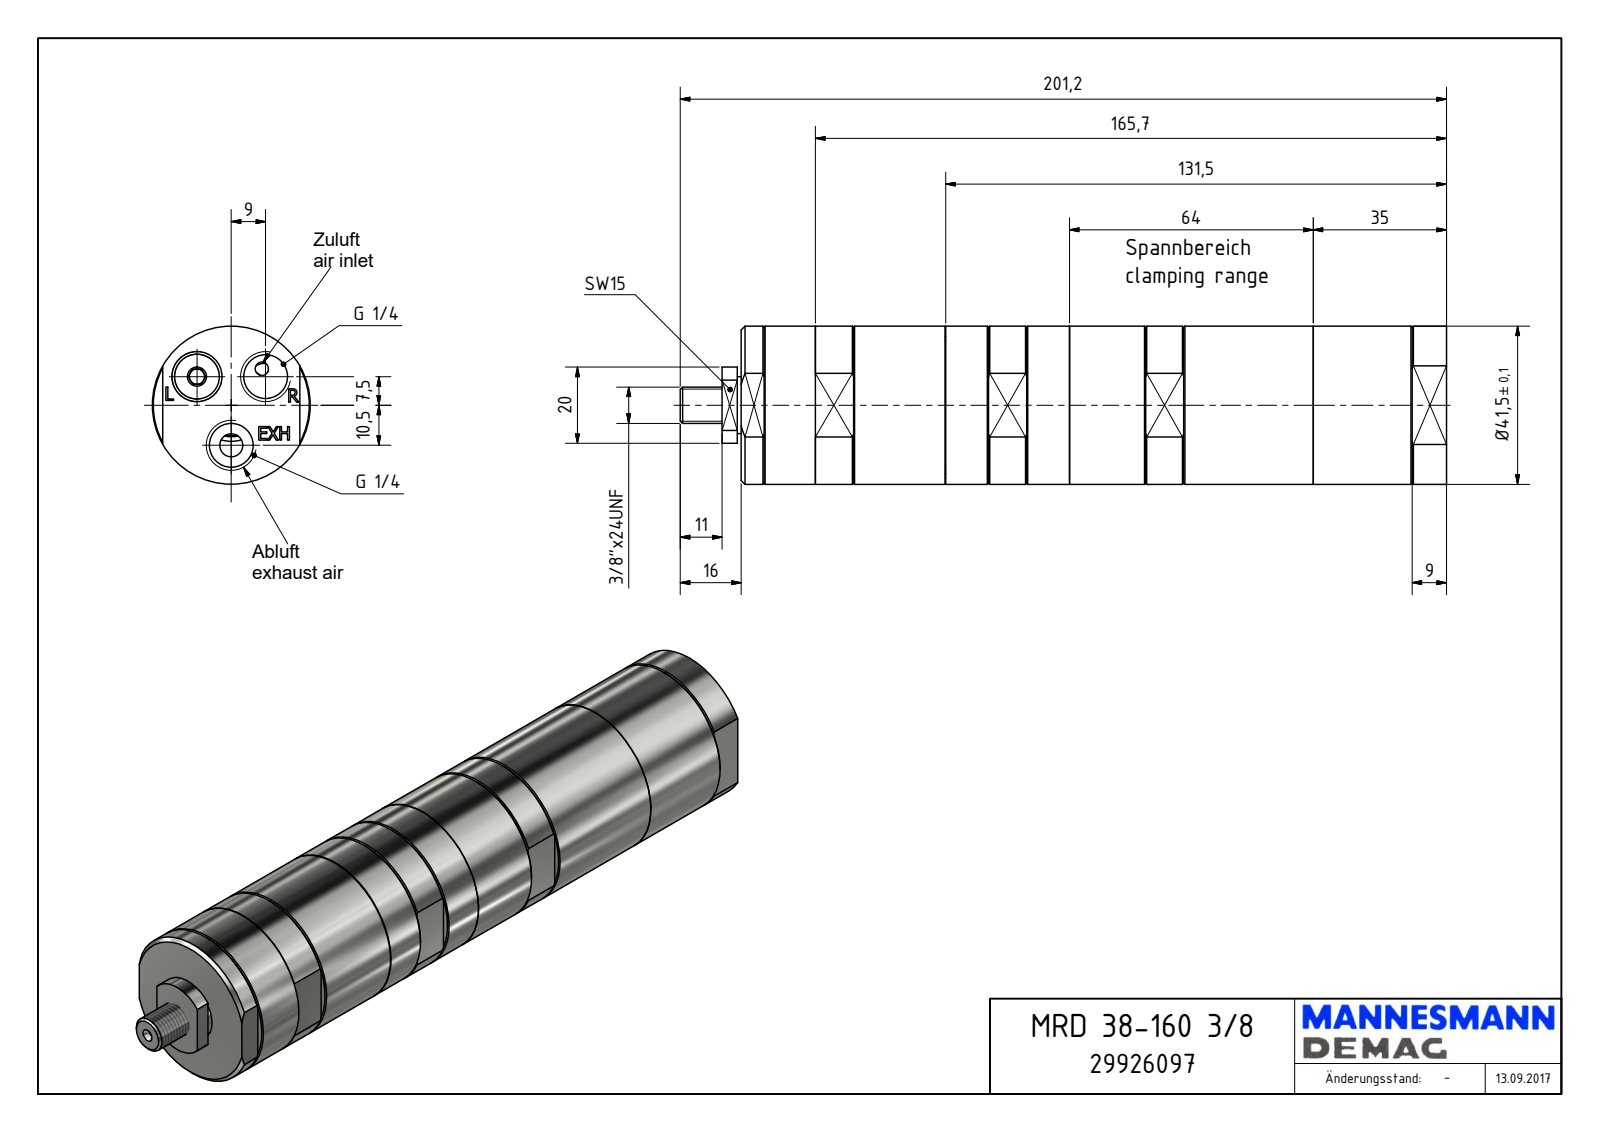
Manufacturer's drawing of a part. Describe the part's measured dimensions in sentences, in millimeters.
The part is named "MRD 38-160 3-8_29926097". Its 3-D file was written by "Autodesk Inventor 2018 (AUTOMOTIVE_DESIGN)". It is 1 solid with 176 faces: 110 planar, 27 cylindrical and 39 other. Overall it measures 201.2 by 41.5 by 41.5 millimeters. Its volume is 248 015 cubic millimeters and its surface area 29 502 square millimeters. Round holes: 2 of diameter 11.45, 1 of diameter 1.6, 1 of diameter 4, 1 of diameter 16. Round bosses or shafts: 1 of diameter 41.5, 1 of diameter 36, 1 of diameter 14.95, 1 of diameter 9.53. Partial cylindrical surfaces (rounded edges, fillets, slot ends): 1 of radius 10. The main face-to-face distances are 185.2, 38, 1, 37, 53.5, 131.7, 53.7, 131.5, 175.23, 121.73. The hole center spacings are 11.72, 20.12, 10.5, 18.
